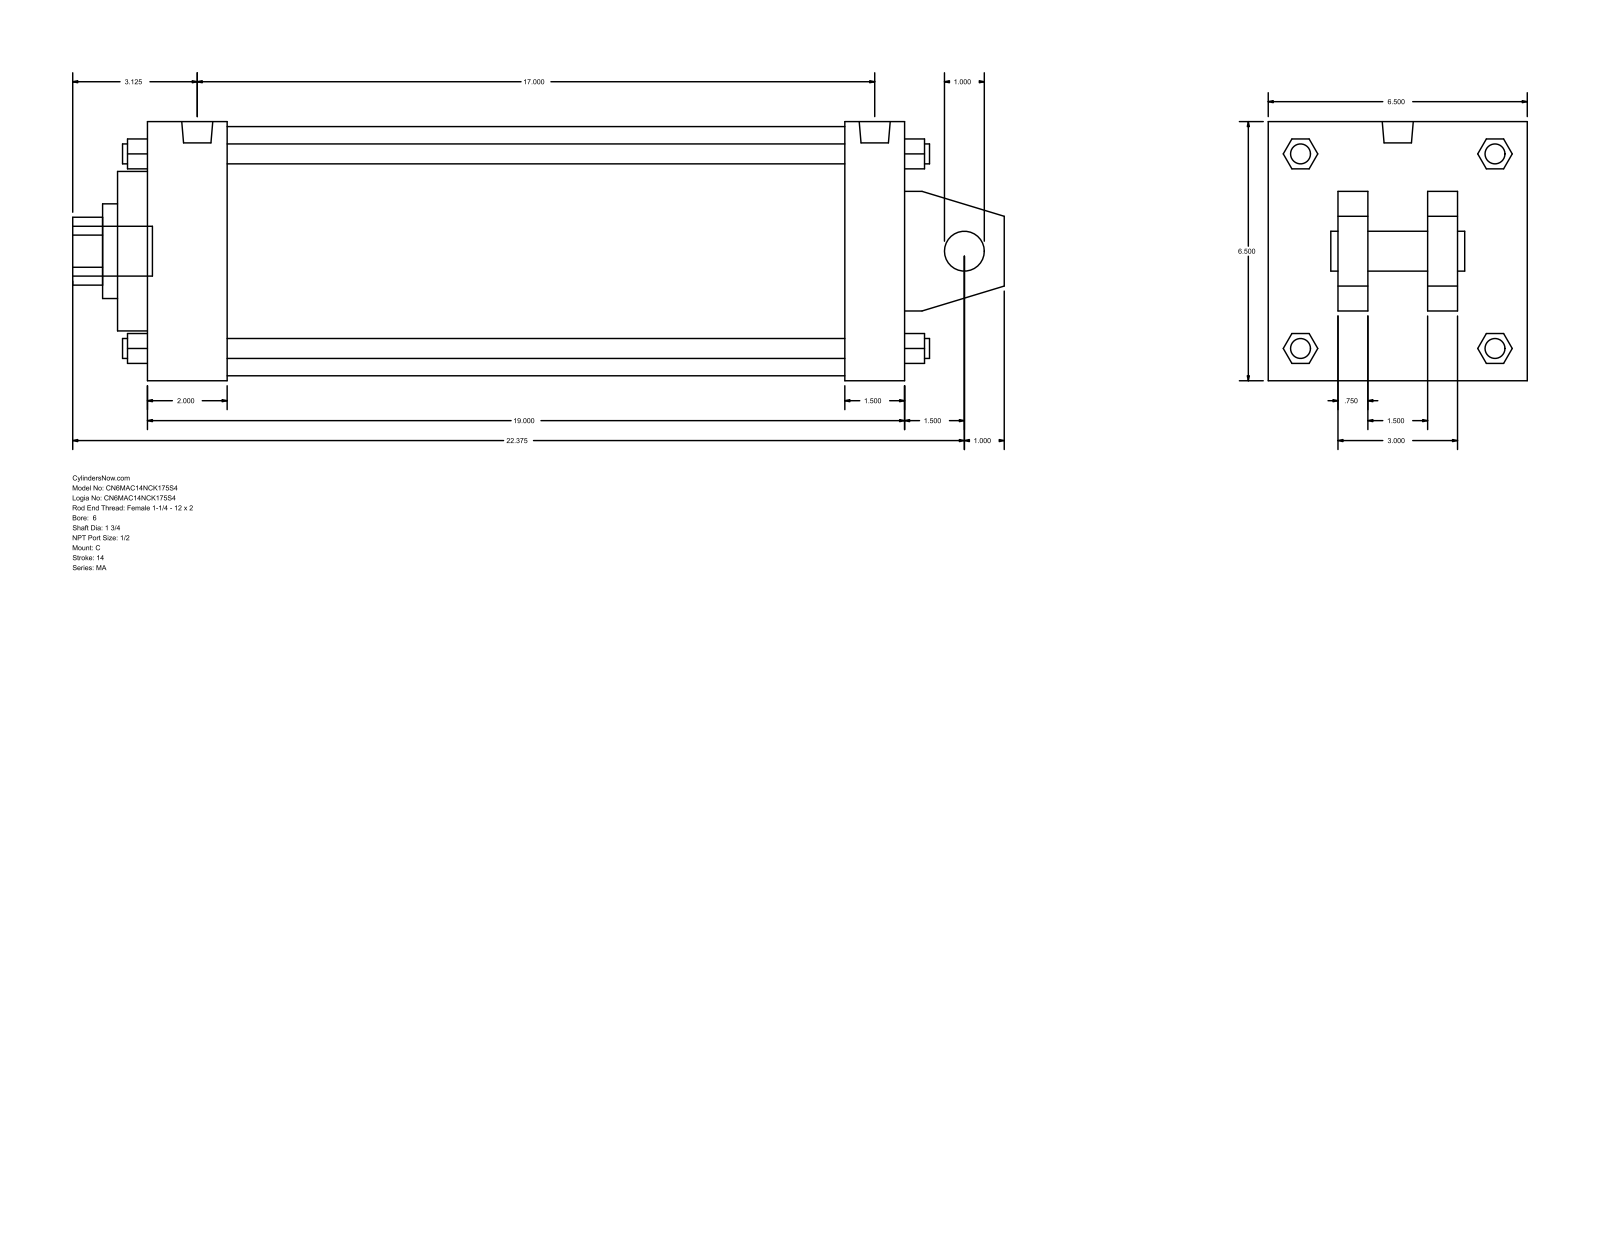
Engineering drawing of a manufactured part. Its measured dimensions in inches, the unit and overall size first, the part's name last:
Units: inches
Overall size (bounding box): 23.375 × 6.5 × 6.5
Round holes (diameter × count): ⌀1 ×1, ⌀1.75 ×1, ⌀2.375 ×1, ⌀4 ×1, ⌀6.25 ×1
Round bosses / shafts (diameter × count): ⌀0.687 ×4, ⌀0.5 ×4, ⌀0.778 ×2, ⌀1.25 ×1
Partial cylindrical surfaces — rounded edges, fillets, slot ends (radius × count): R0.852 ×1
Main face-to-face distances: 6.5, 19, 0.75, 2.5, 4, 2, 1.75, 4.75, 17.5, 2.25
Bodies: 0 solids, 141 faces (109 planar, 32 cylindrical, 0 other)
Part name (STEP PRODUCT): MA_C__0600_1.75
STEP written by: GSSL Pune (CONFIG_CONTROL_DESIGN)
